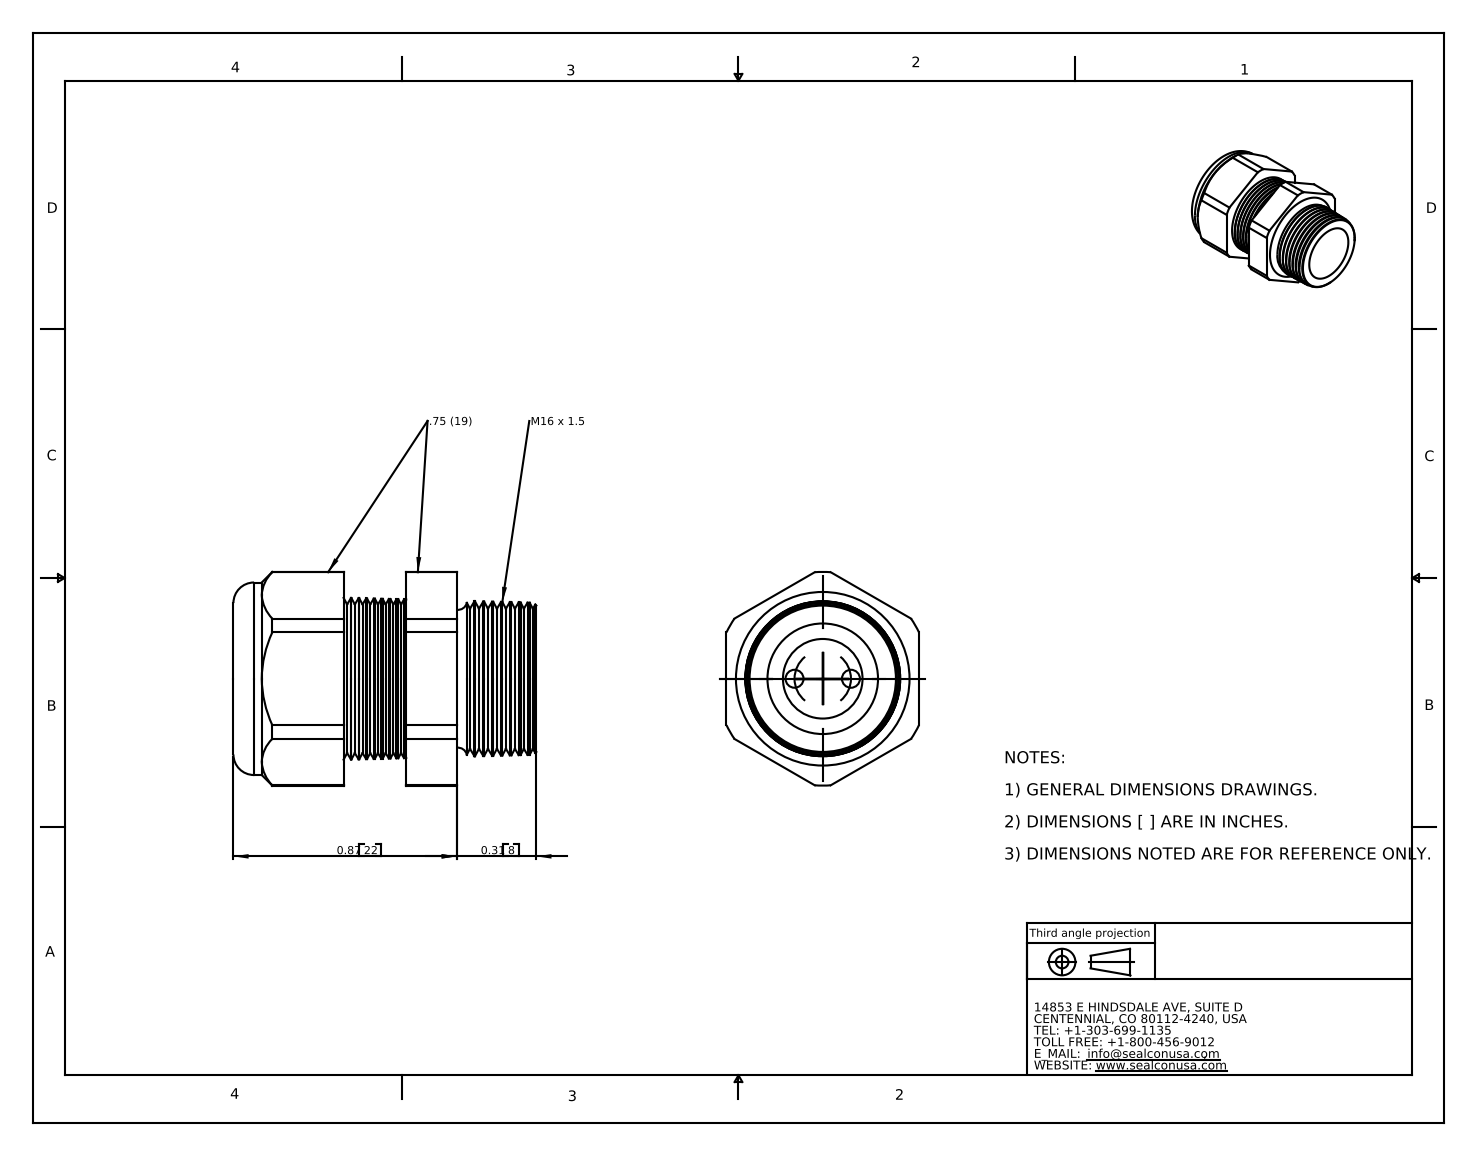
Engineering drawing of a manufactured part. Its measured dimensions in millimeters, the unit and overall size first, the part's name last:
Units: millimetres
Overall size (bounding box): 30 × 21.2 × 19.1
Round holes (diameter × count): ⌀1.8 ×2, ⌀7.4 ×1, ⌀7.9 ×1
Round bosses / shafts (diameter × count): ⌀19.1 ×1
Partial cylindrical surfaces — rounded edges, fillets, slot ends (radius × count): R10.6 ×1
Main face-to-face distances: 19.1, 17.1, 19.1, 10.9, 6.2, 22.1, 11.2, 5, 30, 19.1
Hole centre spacings: 2.8, 5.6
Volume: 5 510 mm³ · Surface area: 3 969 mm²
Bodies: 2 solids, 154 faces (20 planar, 24 cylindrical, 110 other)
Part name (STEP PRODUCT): CD16M4-GY
STEP written by: SolidWorks 2007 (CONFIG_CONTROL_DESIGN)
